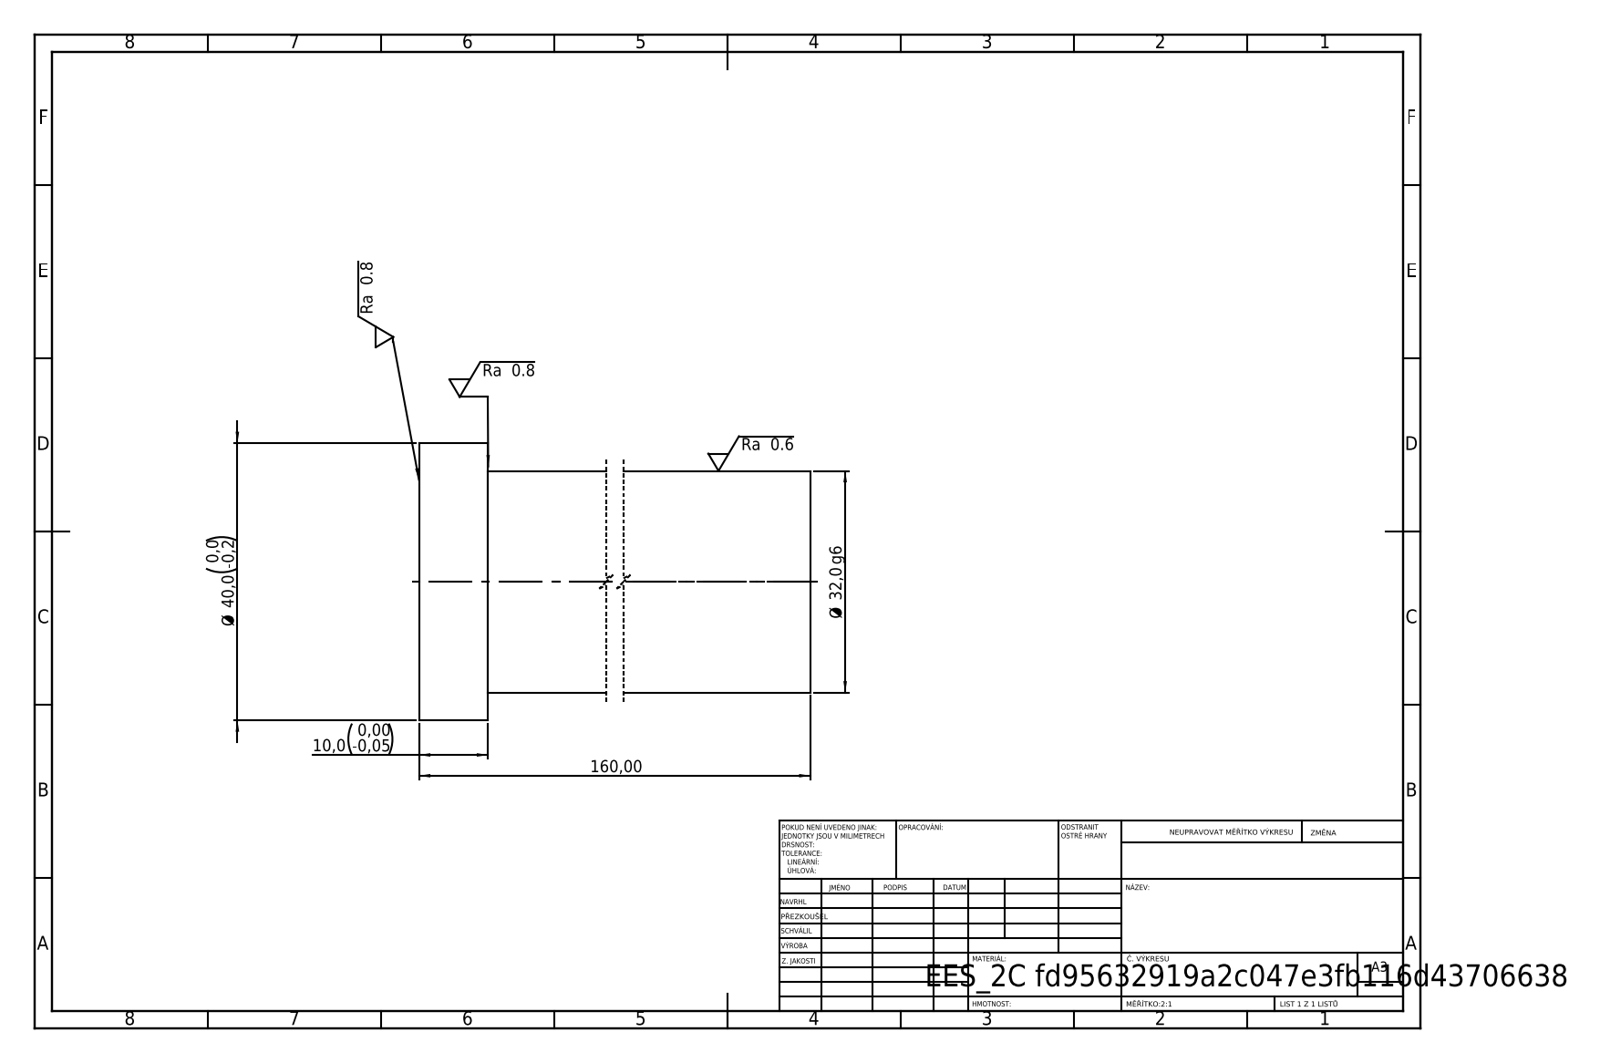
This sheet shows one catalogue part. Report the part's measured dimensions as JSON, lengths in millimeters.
{"step_written_by": "SolidWorks 2019 (CONFIG_CONTROL_DESIGN)", "units": "millimeters", "bodies": {"solids": 1, "faces": 7, "planar": 3, "cylindrical": 4, "other": 0}, "overall_size": [160, 40, 40], "volume_mm3": 133204, "surface_area_mm2": 18850, "round_bosses_or_shafts": [[40, 1], [32, 1]], "face_to_face_distances": [160, 10, 150]}
